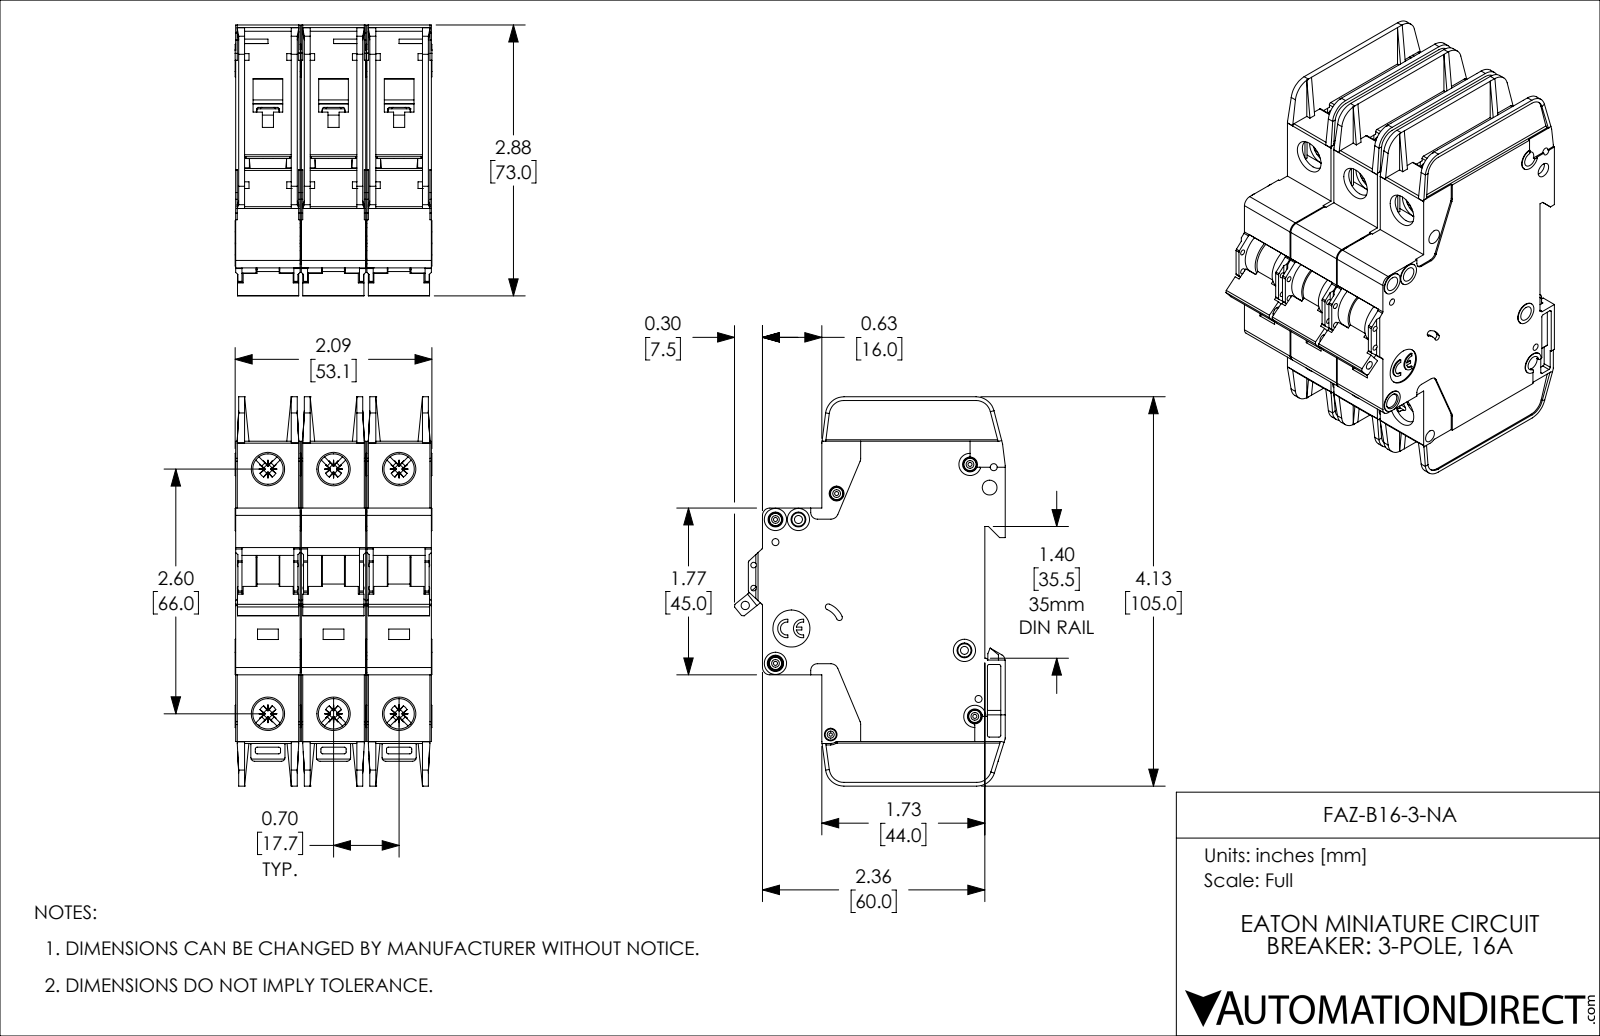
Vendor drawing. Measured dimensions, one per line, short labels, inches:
name: FAZ-B16-3-NA
written by: SolidWorks 2019 (AUTOMOTIVE_DESIGN)
unit: in
bodies: 3 solids, 3381 faces (2013 planar, 1071 cylindrical, 297 other)
size: 4.134 × 2.876 × 2.091
volume: 14.05 in³; area: 123 in²
holes: 8× ⌀0.157, 6× ⌀0.323, 5× ⌀0.043, 4× ⌀0.075, 2× ⌀0.059, 2× ⌀0.085, 1× ⌀0.035, 1× ⌀0.089, 1× ⌀0.098, 1× ⌀0.134, 1× ⌀0.394
bosses: 5× ⌀0.13, 4× ⌀0.236, 4× ⌀0.118, 3× ⌀0.098
rounds: 72× R0.02, 30× R0.016, 18× R0.039, 12× R0.043, 12× R0.079, 6× R0.008, 6× R0.01, 6× R0.028
face distances: 0.697, 0.047, 1.394, 0.685, 0.591, 1.382, 0.744, 0.65, 0.106, 0.094
hole spacings: 0.697, 2.69, 2.598, 0.244, 0.537, 0.87, 1.394, 2.948
